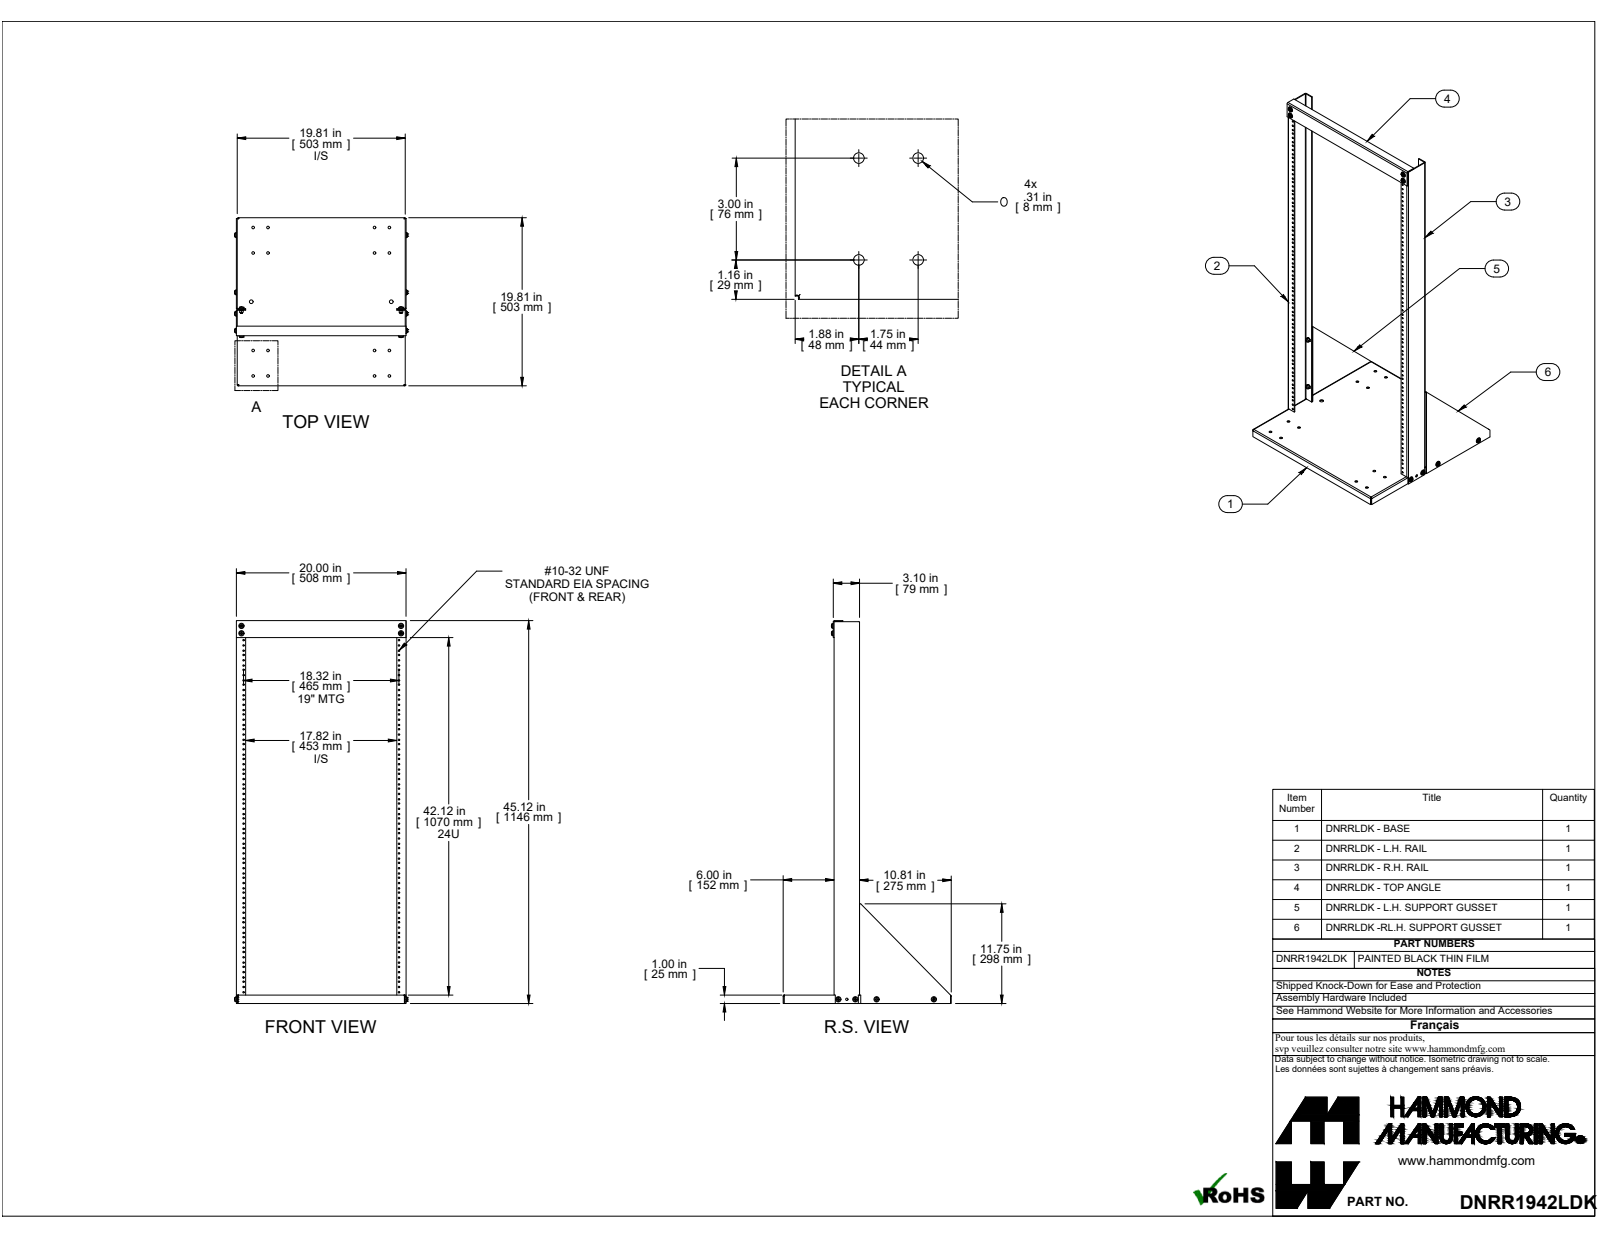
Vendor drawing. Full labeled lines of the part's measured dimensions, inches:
Part name (STEP PRODUCT): DNRR1942LDK
STEP written by: SolidWorks 2019 (CONFIG_CONTROL_DESIGN)
Units: inches
Bodies: 54 solids, 990 faces (584 planar, 302 cylindrical, 104 other)
Overall size (bounding box): 45.125 × 20.398 × 19.812
Volume: 106.7 in³ · Surface area: 2 308 in²
Round holes (diameter × count): ⌀0.177 ×144, ⌀0.313 ×18, ⌀0.281 ×15, ⌀0.196 ×12, ⌀0.282 ×12, ⌀0.437 ×2
Round bosses / shafts (diameter × count): ⌀0.468 ×12, ⌀0.25 ×12, ⌀0.625 ×6, ⌀0.625 ×6
Partial cylindrical surfaces — rounded edges, fillets, slot ends (radius × count): R0.048 ×11, R0.143 ×11, R0.156 ×4
Main face-to-face distances: 0.095, 0.095, 19.907, 19.812, 20.002, 3, 0.19, 2.905, 2.81, 2.905
Hole centre spacings: 1.75, 3.5, 5.25, 3, 7, 8.75, 10.5, 0.625
